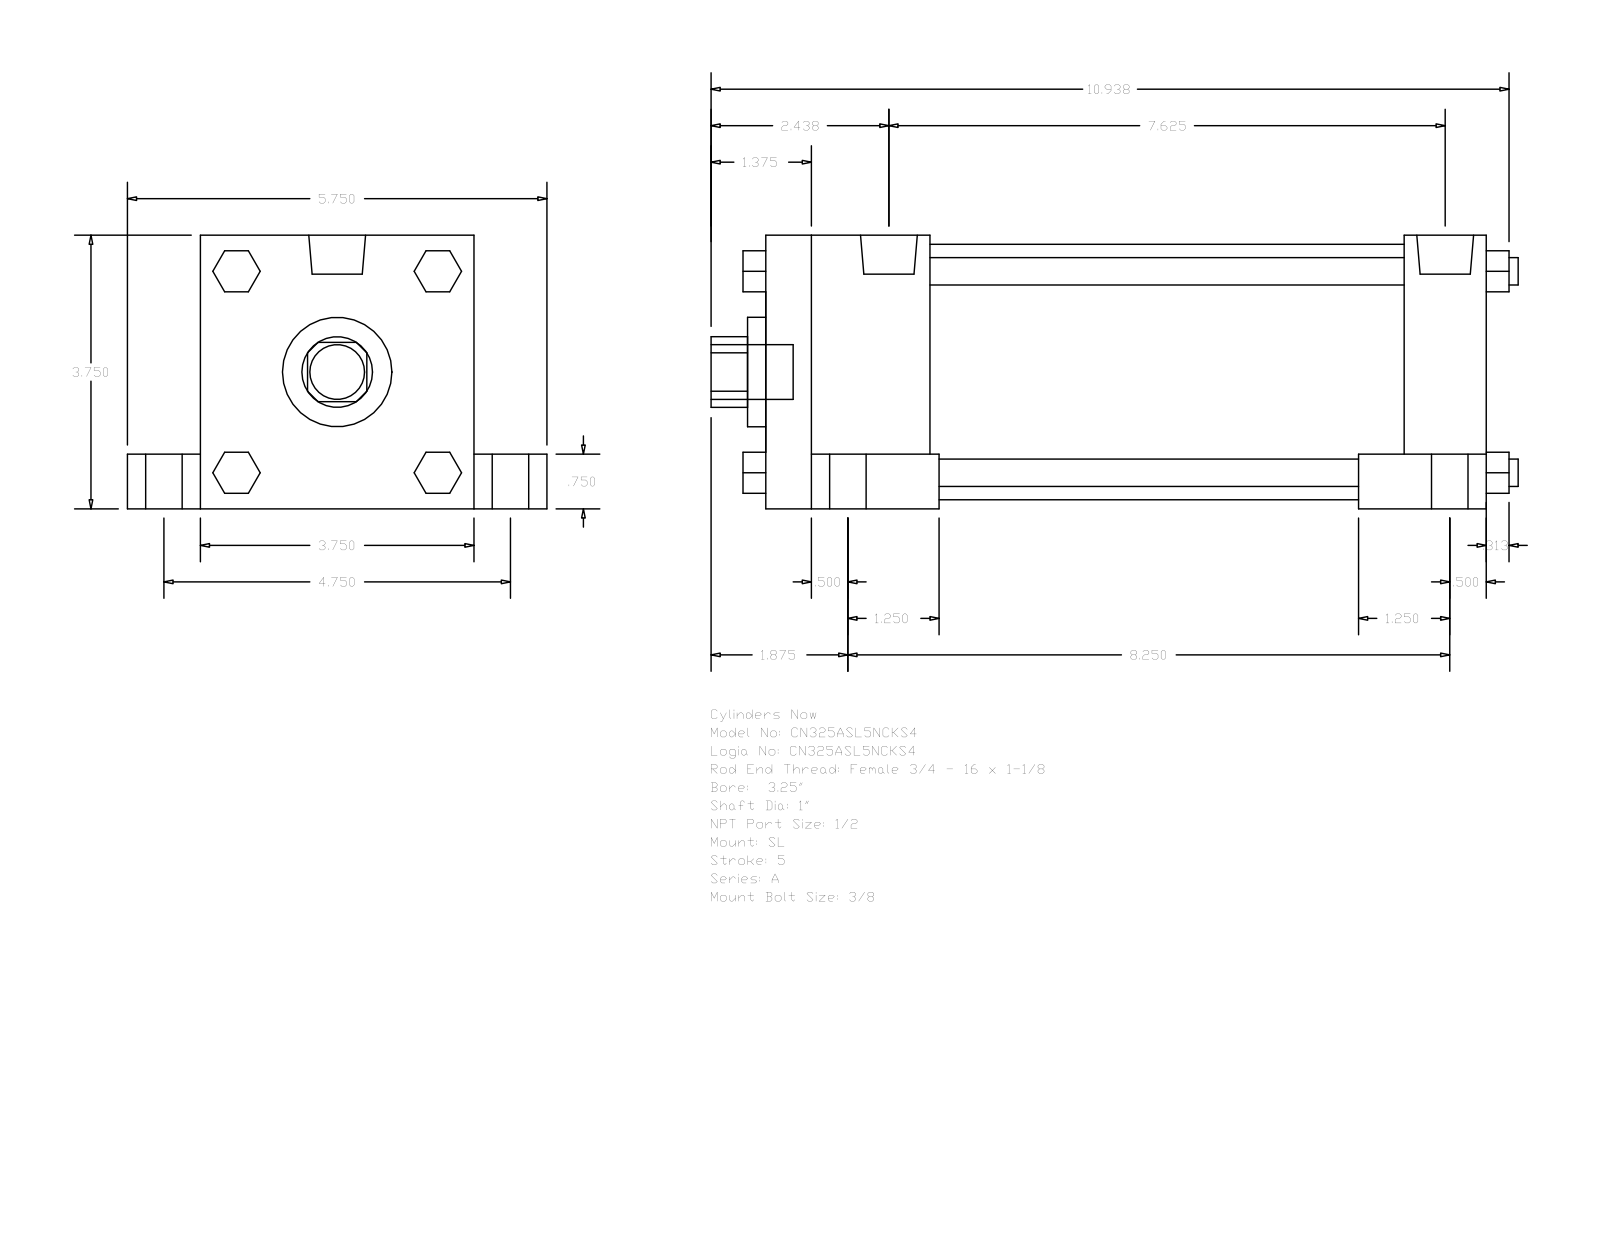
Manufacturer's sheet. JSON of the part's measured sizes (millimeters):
{"part_name": "A_SL__0325_1", "step_written_by": "GSSL Pune (CONFIG_CONTROL_DESIGN)", "units": "millimeters", "bodies": {"solids": 0, "faces": 150, "planar": 114, "cylindrical": 36, "other": 0}, "overall_size": [280.99, 146.05, 95.25], "round_holes": [[25.4, 1], [38.1, 1], [88.9, 1]], "round_bosses_or_shafts": [[19.05, 5], [12.7, 4], [9.53, 4], [8.73, 4], [19.77, 2]], "partial_cylinders_radius": [[12.29, 1]], "face_to_face_distances": [95.24, 250.83, 19.05, 25.41, 120.65, 76.19, 15.87, 57.15, 222.25, 165.1]}
